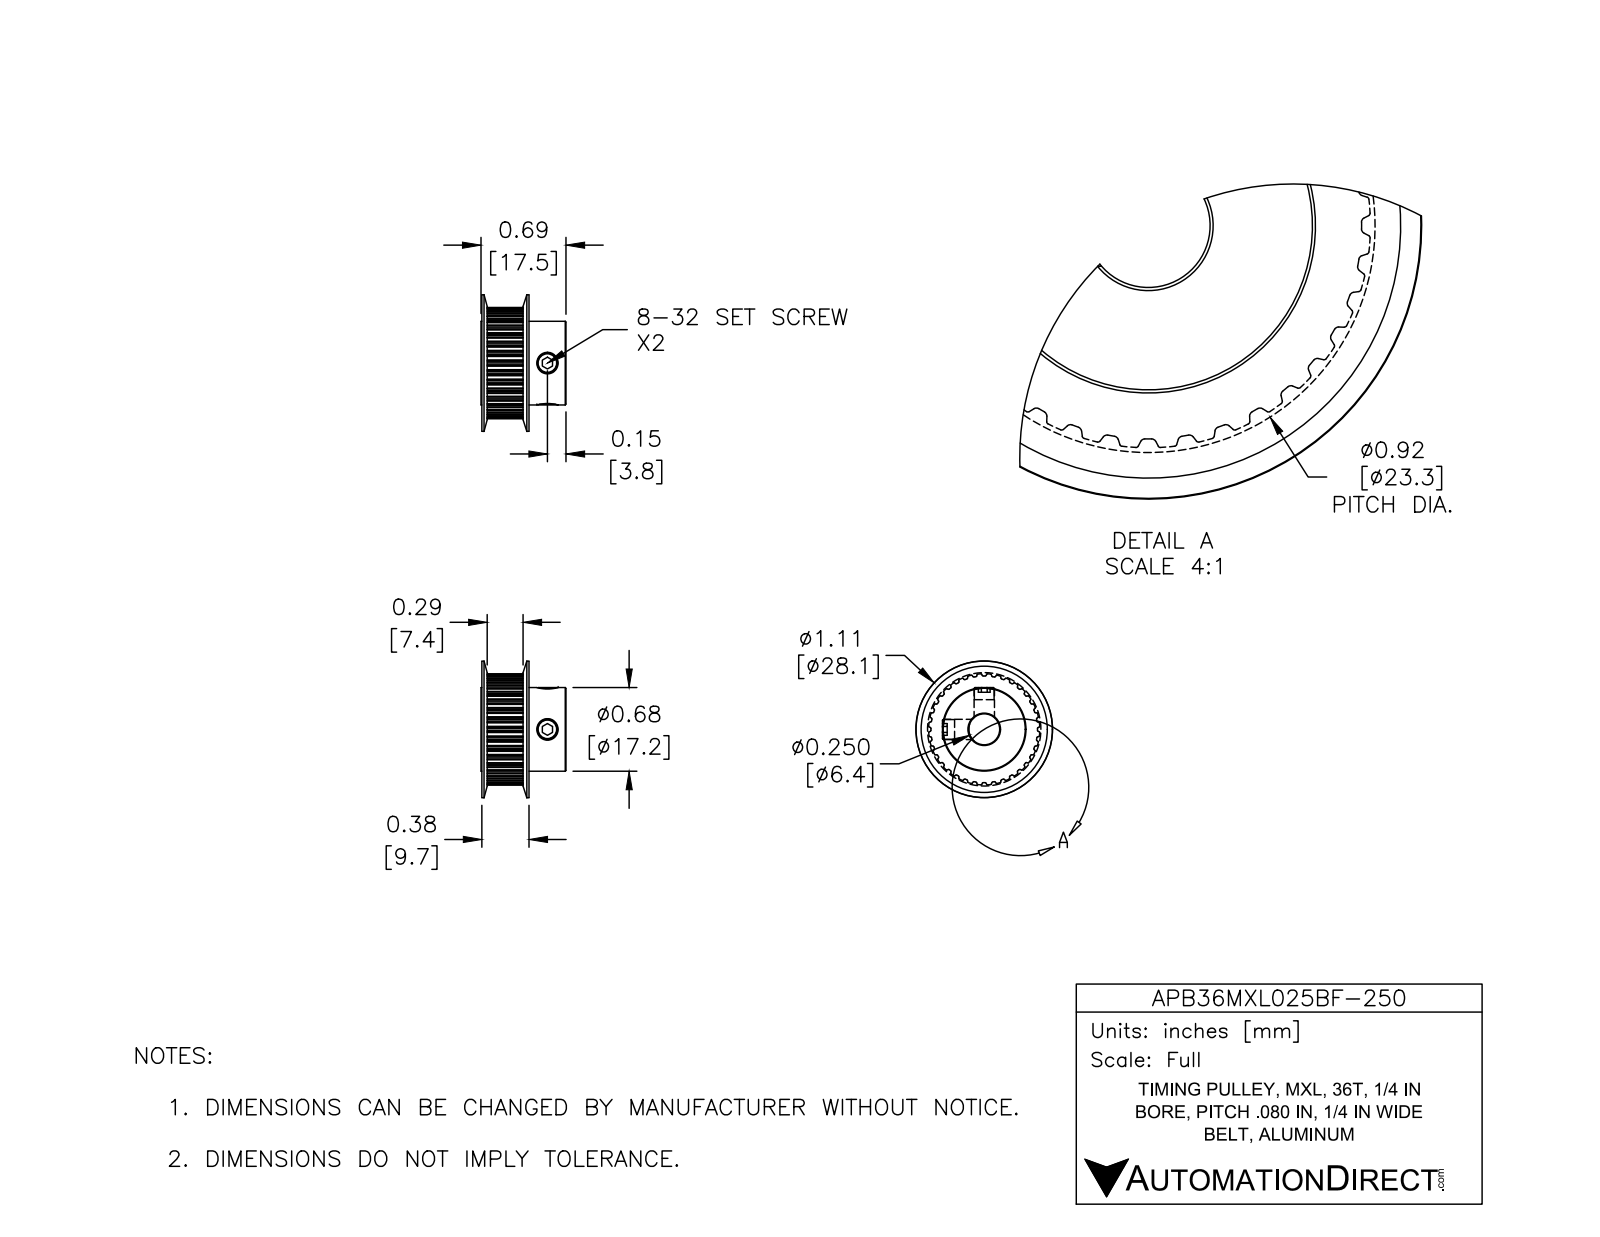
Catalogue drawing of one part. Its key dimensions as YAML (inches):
part_name: "APB36MXL025BF-250"
step_written_by: "SolidWorks 2016 (AUTOMOTIVE_DESIGN)"
units: inches
bodies: {solids: 3, faces: 381, planar: 96, cylindrical: 259, other: 26}
overall_size: [1.105, 1.105, 0.688]
volume: 0.308
surface_area: 5.27
round_holes:
  - {diameter: 0.164, count: 2}
  - {diameter: 0.25, count: 1}
round_bosses_or_shafts:
  - {diameter: 0.16, count: 2}
  - {diameter: 0.676, count: 1}
partial_cylinders:
  - {radius: 0.005, count: 72}
  - {radius: 0.009, count: 72}
  - {radius: 0.431, count: 1}
  - {radius: 0.449, count: 1}
face_to_face_distances: [0.346, 0.025, 0.37, 0.687, 0.663, 0.317, 0.383, 0.382, 0.05, 0.025]
